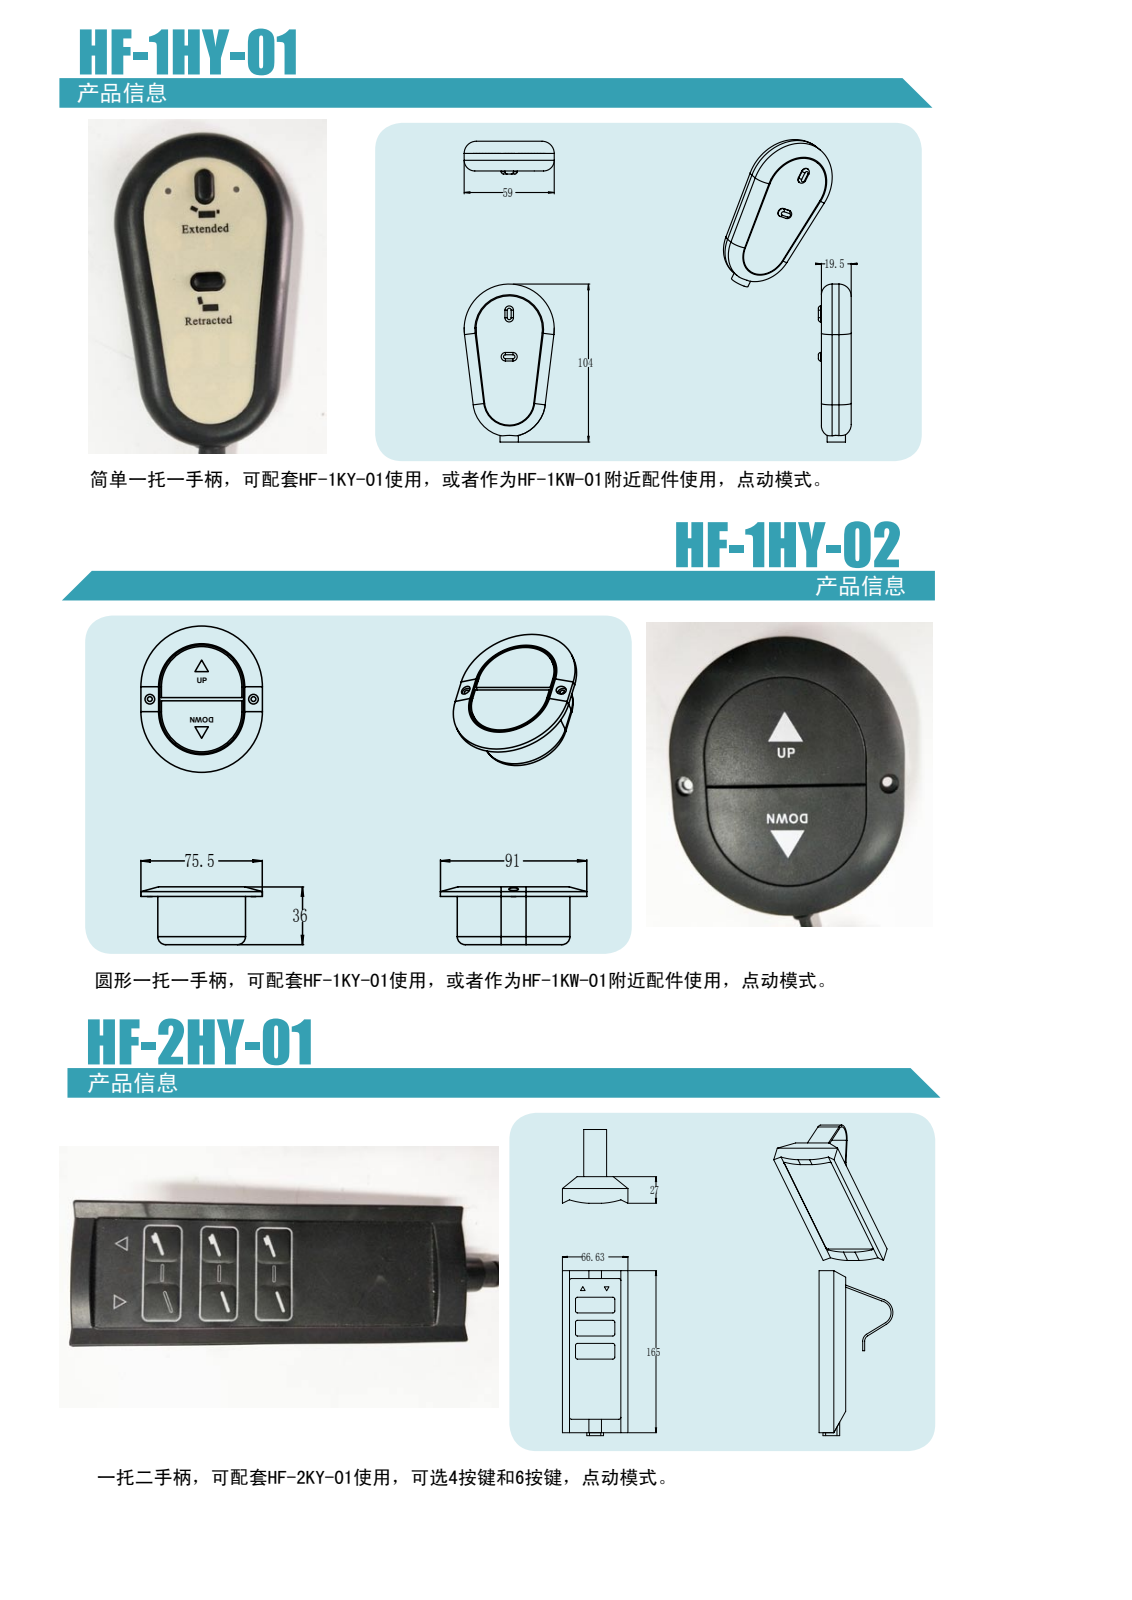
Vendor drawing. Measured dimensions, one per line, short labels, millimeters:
name: HF-2HY-01
written by: PRO/ENGINEER BY PARAMETRIC TECHNOLOGY CORPORATION, 2008380 (CONFIG_CONTROL_DESIGN)
unit: mm
bodies: 1 solid, 46 faces (30 planar, 16 cylindrical, 0 other)
size: 4267.2 × 1907.4 × 1692.4
volume: 3 775 000 000 mm³; area: 24 070 000 mm²
holes: 1× ⌀292.1
bosses: 1× ⌀431.8
rounds: 4× R50.8, 2× R1912.6, 1× R160.8, 1× R211.6, 1× R308.4, 1× R355.6
face distances: 586.5, 1692.4, 50.3, 4191, 550.5, 1141.9, 688.1, 101.6, 50.8, 490.2
